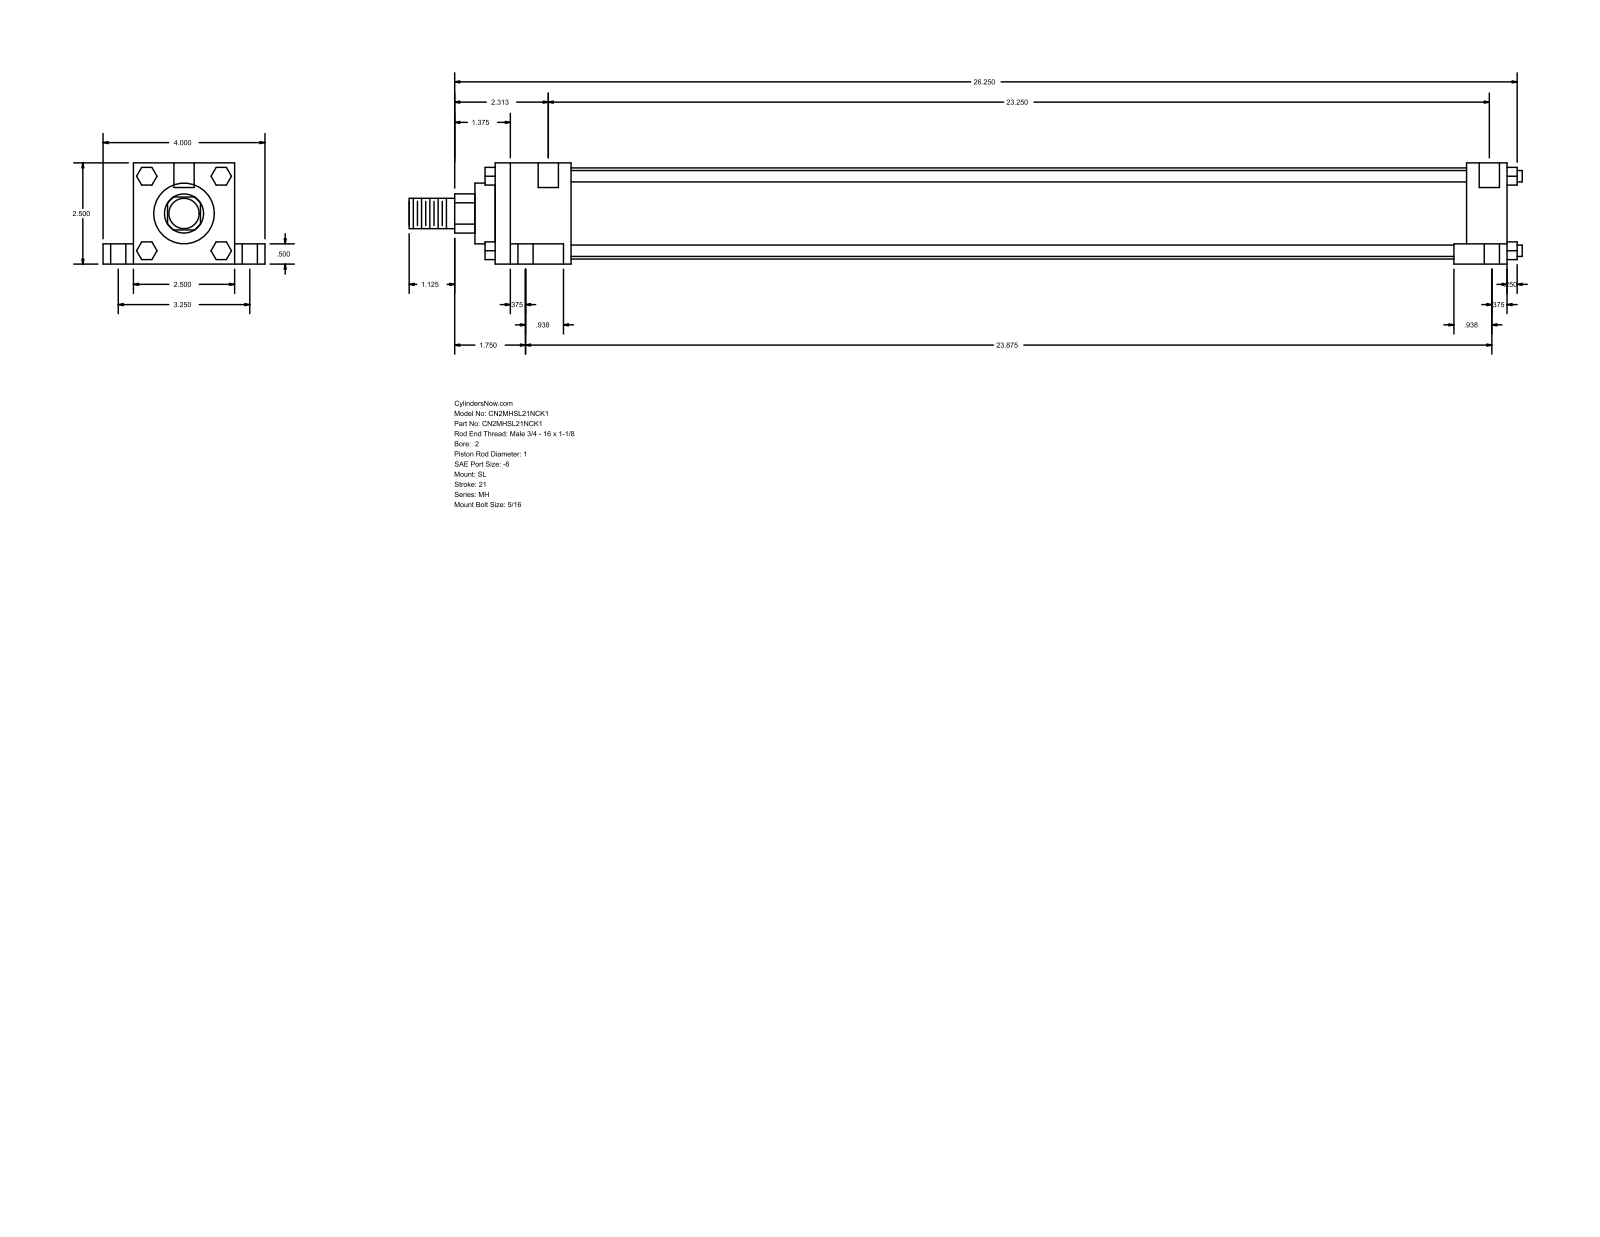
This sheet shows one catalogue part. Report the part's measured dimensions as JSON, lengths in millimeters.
{"part_name": "MH_SL__0200_1", "step_written_by": "GSSL Pune (CONFIG_CONTROL_DESIGN)", "units": "millimeters", "bodies": {"solids": 0, "faces": 148, "planar": 112, "cylindrical": 36, "other": 0}, "overall_size": [698.5, 101.6, 63.5], "round_holes": [[5.56, 4], [9.53, 4], [15.88, 4], [12.7, 2]], "round_bosses_or_shafts": [[7.14, 4], [57.15, 1], [38.1, 1], [25.4, 1], [19.05, 1]], "partial_cylinders_radius": [[12.29, 1]], "face_to_face_distances": [63.5, 635, 12.7, 19.05, 50.8, 82.55, 25.4, 609.6, 47.63, 561.97], "hole_center_spacings": [41.3, 42.36, 43.67, 82.54, 593.58, 598.33, 598.48, 606.25]}
